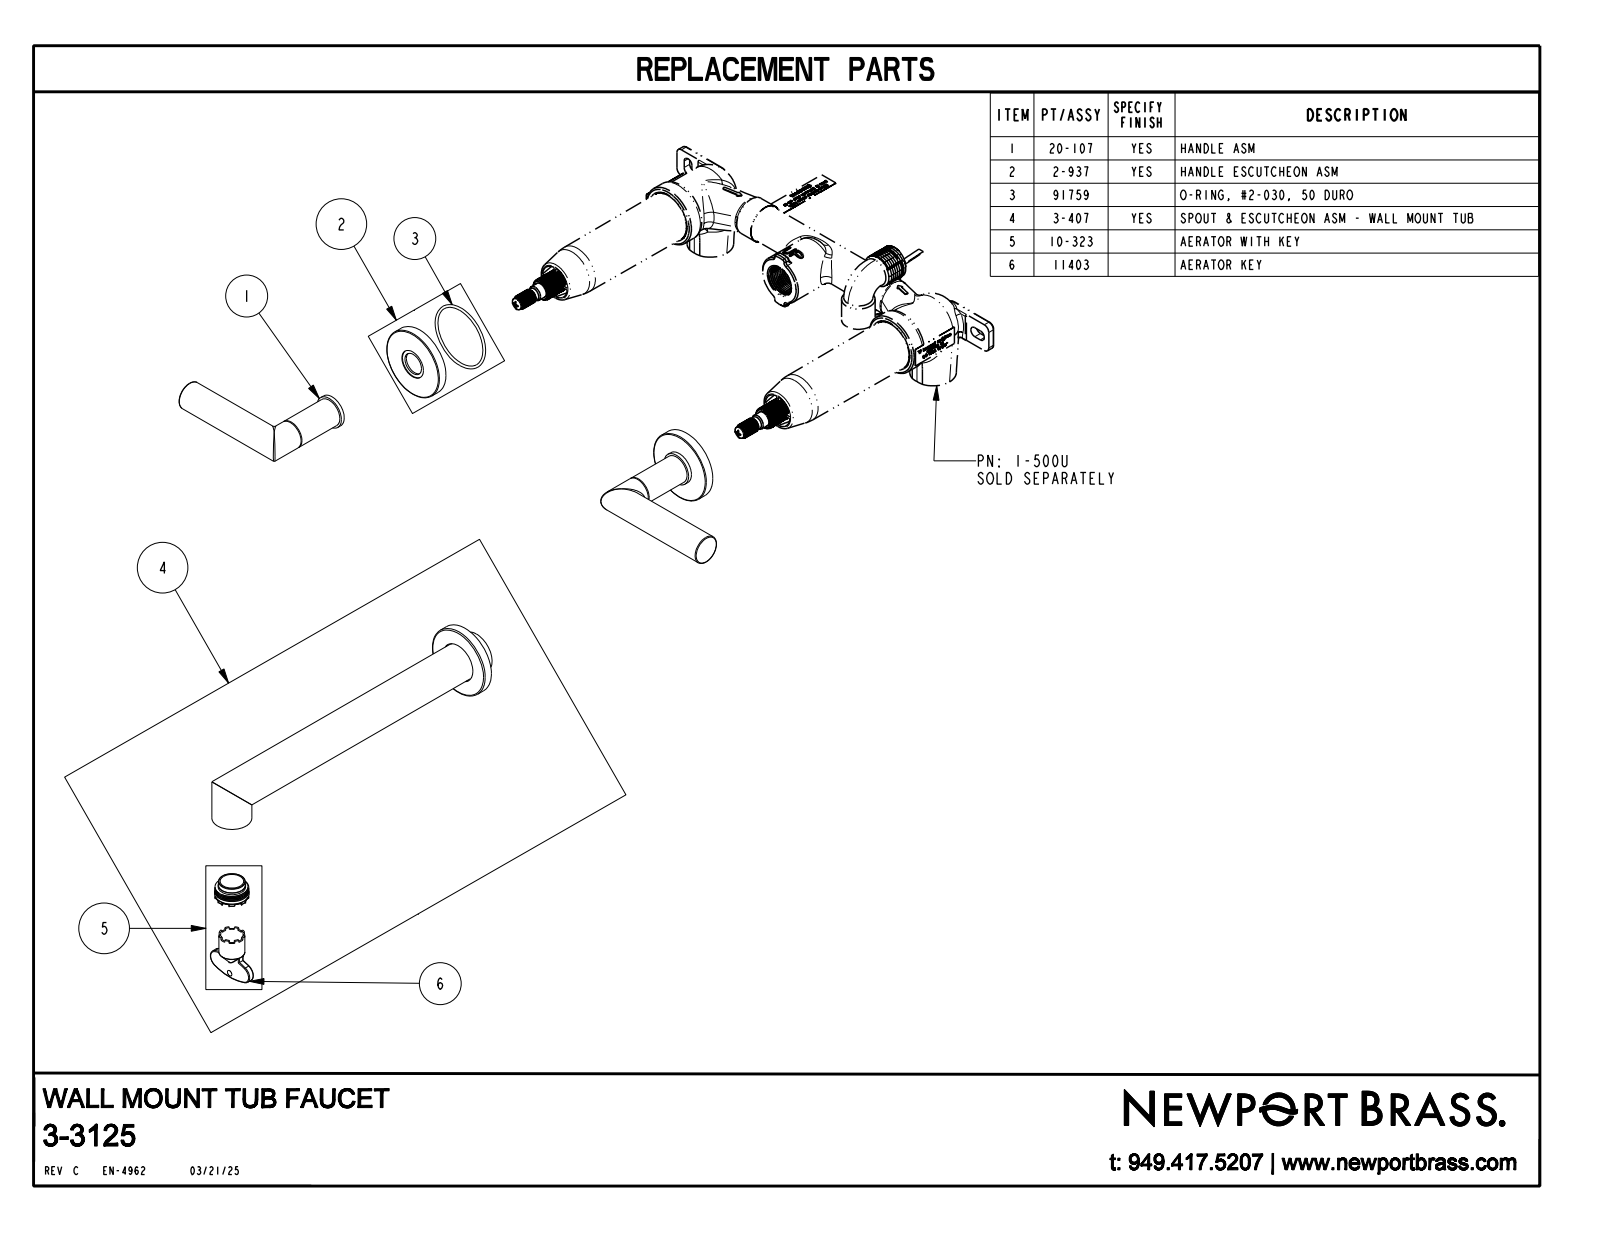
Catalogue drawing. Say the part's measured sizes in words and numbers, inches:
The part is named "3-3125_SW0001". Its 3-D file was written by "CREO PARAMETRIC BY PTC INC, 2018400 (AUTOMOTIVE_DESIGN)". It is 5 solids with 69 faces: 19 planar, 30 cylindrical and 20 other. Overall it measures 13.875 by 8.75 by 7.8 inches. Its volume is 13.29 cubic inches and its surface area 74.79 square inches. Round bosses or shafts: 3 of diameter 0.75, 2 of diameter 1.85, 2 of diameter 1, 2 of diameter 0.86, 2 of diameter 0.5, 1 of diameter 1.75. The main face-to-face distances are 0.25, 0.261, 1.701, 1.732, 1.451, 1.482, 1.44, 1.471, 0.031, 13.875.
